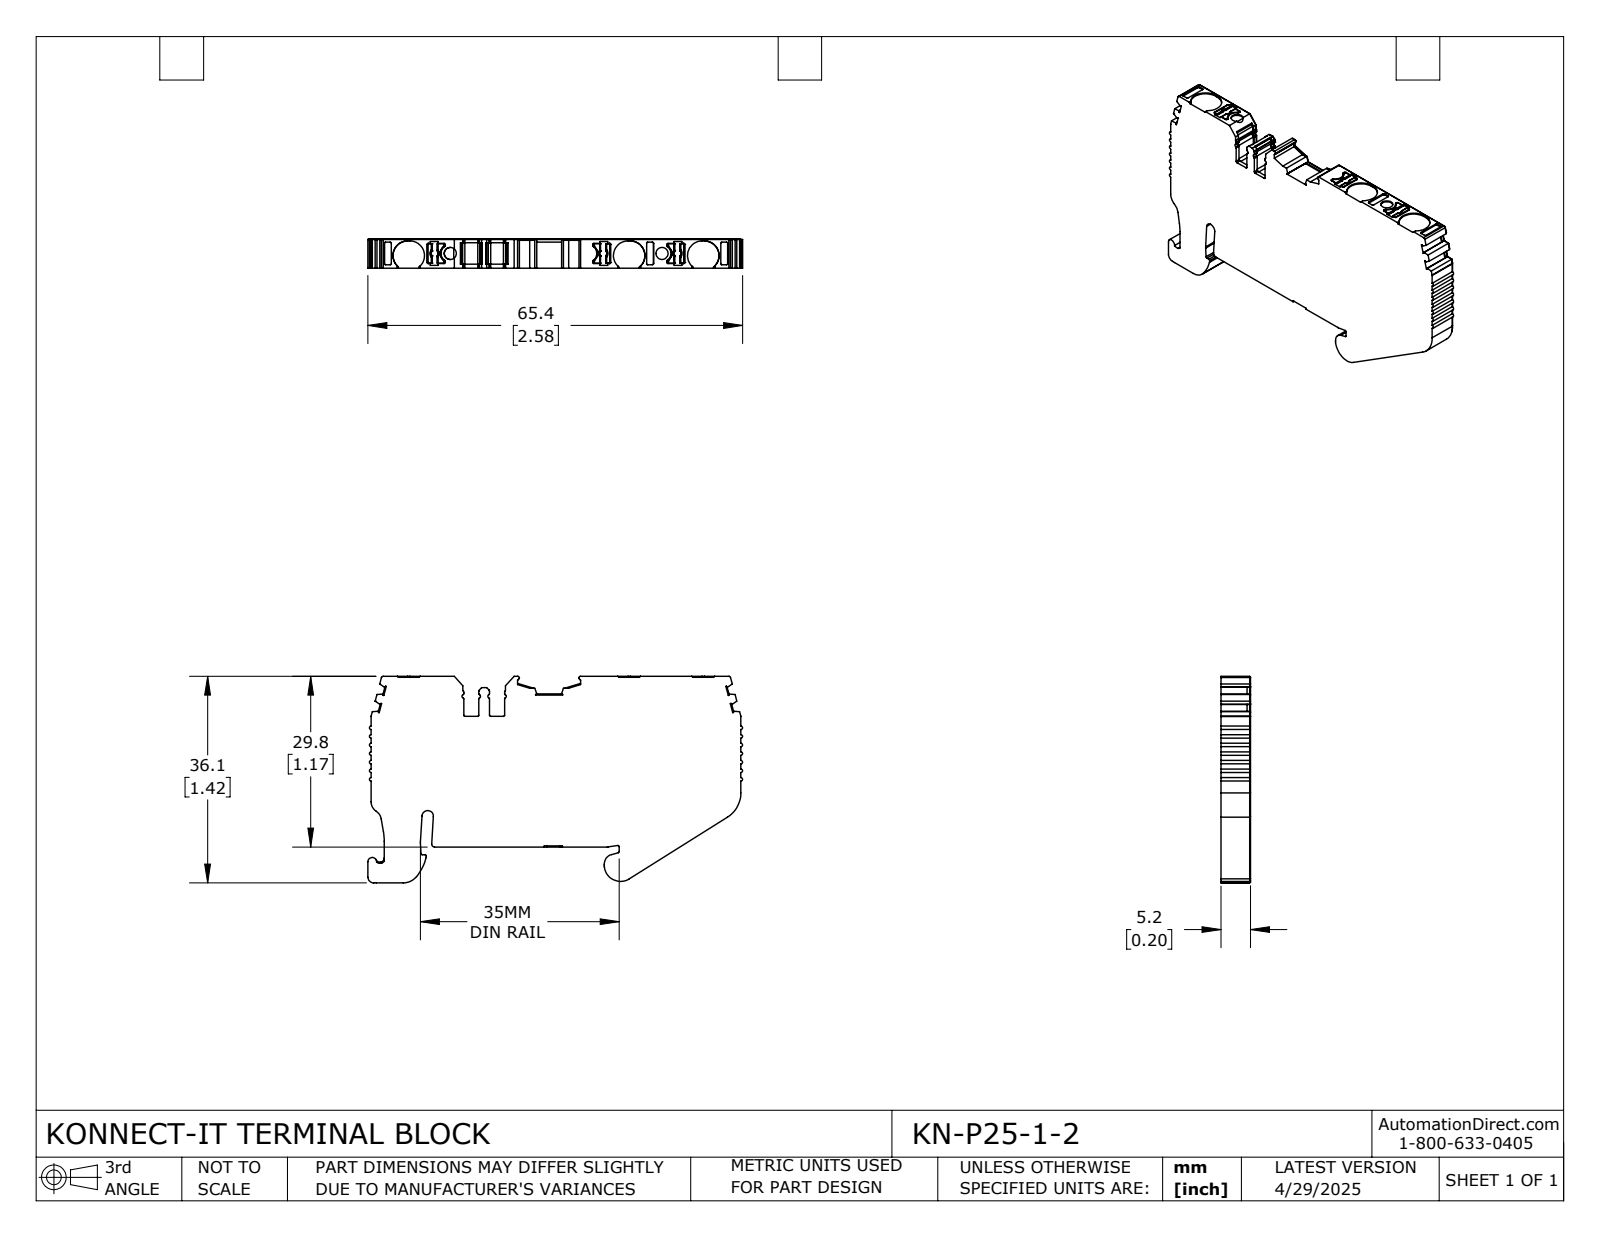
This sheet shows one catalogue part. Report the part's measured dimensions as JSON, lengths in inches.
{"part_name": "KN-P25-1-2", "step_written_by": "SolidWorks 2024 (CONFIG_CONTROL_DESIGN)", "units": "inches", "bodies": {"solids": 1, "faces": 655, "planar": 345, "cylindrical": 259, "other": 51}, "overall_size": [2.576, 1.42, 0.203], "volume_in3": 0.584, "surface_area_in2": 7.967, "round_holes": [[0.083, 2]], "partial_cylinders_radius": [[0.008, 66], [0.012, 39], [0.004, 19], [0.02, 18], [0.006, 12], [0.016, 9], [0.1, 6], [0.039, 3]], "face_to_face_distances": [0.203, 1.166, 1.174, 2.543, 0.177, 0.197, 0.246, 1.412, 0.079, 1.42], "hole_center_spacings": [1.456]}
